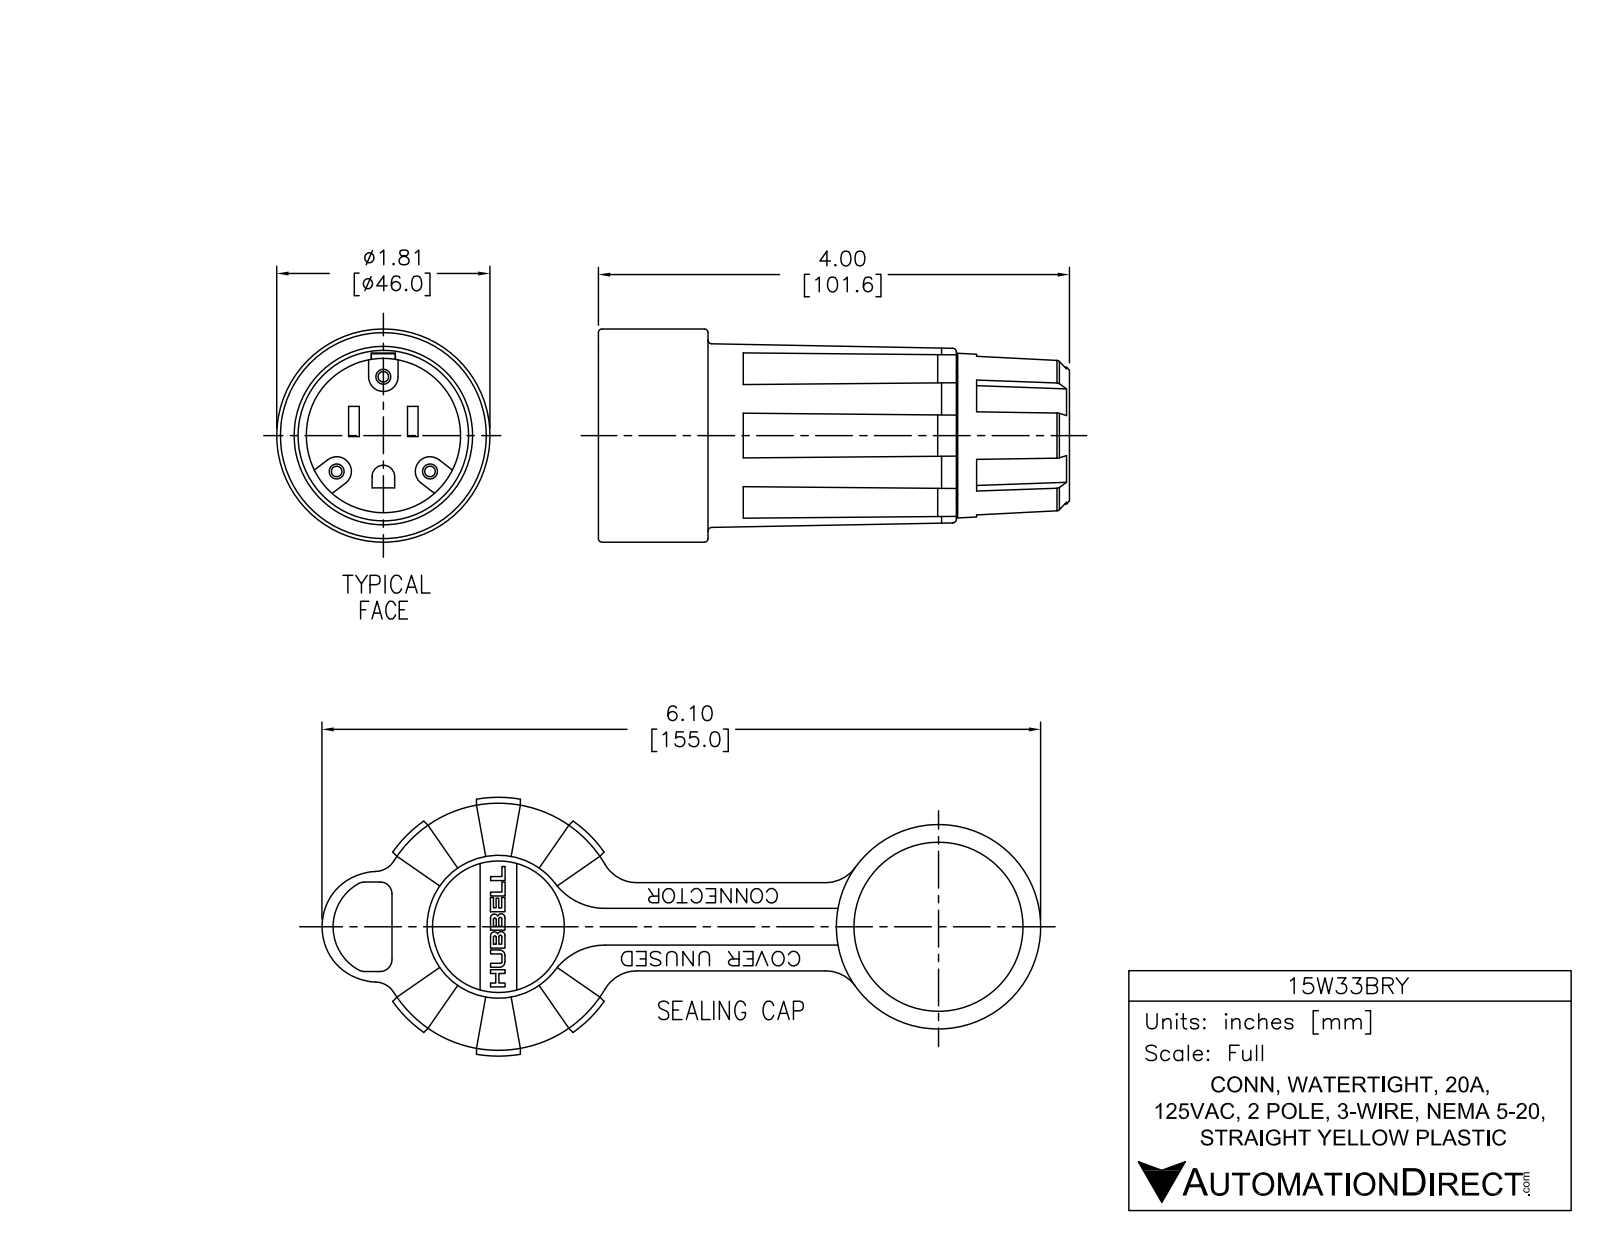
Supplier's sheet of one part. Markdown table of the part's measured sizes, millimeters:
| quantity | value |
| --- | --- |
| part name | 15W33BRY |
| STEP written by | SolidWorks 2013 (AUTOMOTIVE_DESIGN) |
| units | millimeters |
| bodies | 1 solid, 389 faces (189 planar, 89 cylindrical, 111 other) |
| overall size | 157.5 × 104.3 × 55.9 |
| volume | 122 800 mm³ |
| surface area | 38 550 mm² |
| round holes (diameter × count) | 15.9 × 1, 29.2 × 1, 30.5 × 1, 38.1 × 1, 47 × 1 |
| round bosses / shafts (diameter × count) | 5.1 × 3, 47.5 × 1, 46.4 × 1, 39.6 × 1, 37.8 × 1, 33.8 × 1, 25.4 × 1 |
| partial cylindrical surfaces (radius × count) | 0.4 × 16, 6.4 × 4, 1.4 × 3, 2.8 × 3, 2.5 × 2, 3 × 2, 2.7 × 1, 9.5 × 1 |
| main face-to-face distances | 3.6, 1.5, 11.4, 2, 1.3, 7.6, 55.9, 52.3, 53.8, 4.2 |
| hole center spacings | 96.5 |
